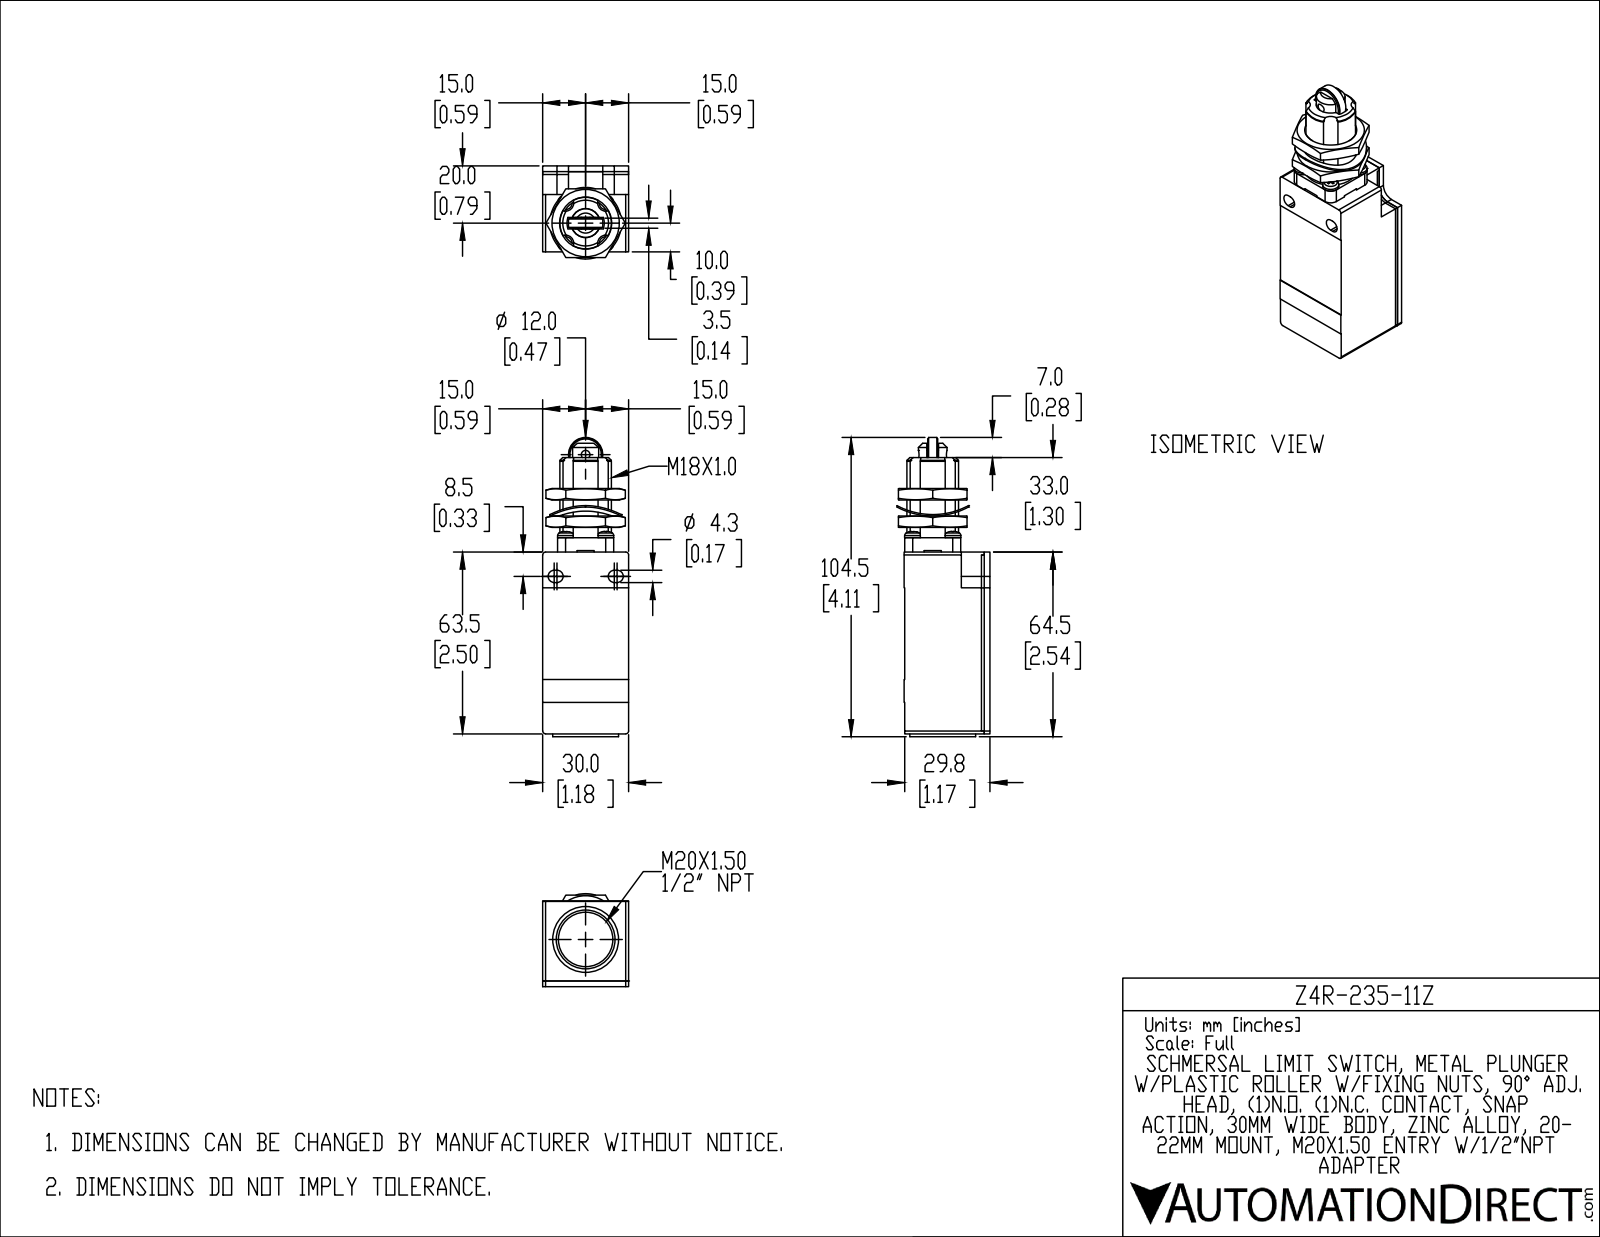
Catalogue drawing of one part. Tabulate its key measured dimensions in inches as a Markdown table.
| quantity | value |
| --- | --- |
| part name | Z4R-235-11Z |
| STEP written by | SolidWorks 2019 (AUTOMOTIVE_DESIGN) |
| units | inches |
| bodies | 2 solids, 389 faces (265 planar, 95 cylindrical, 29 other) |
| overall size | 4.114 × 1.279 × 1.181 |
| volume | 3.806 in³ |
| surface area | 26.23 in² |
| round holes (diameter × count) | 0.276 × 3, 0.118 × 1, 0.512 × 1, 0.545 × 1, 0.732 × 1, 0.748 × 1 |
| round bosses / shafts (diameter × count) | 0.213 × 4, 0.256 × 3, 0.984 × 1, 0.906 × 1, 0.472 × 1, 0.415 × 1, 0.394 × 1, 0.276 × 1 |
| partial cylindrical surfaces (radius × count) | 0.02 × 12, 0.039 × 4, 0.085 × 4, 0.11 × 4, 0.11 × 4, 0.157 × 2, 0.159 × 2, 1.043 × 2 |
| main face-to-face distances | 1.181, 1.173, 0.157, 2.5, 0.079, 0.378, 0.945, 0.207, 2.293, 0.15 |
| hole center spacings | 2.228, 3.706, 0.138, 0.866, 1.496 |
